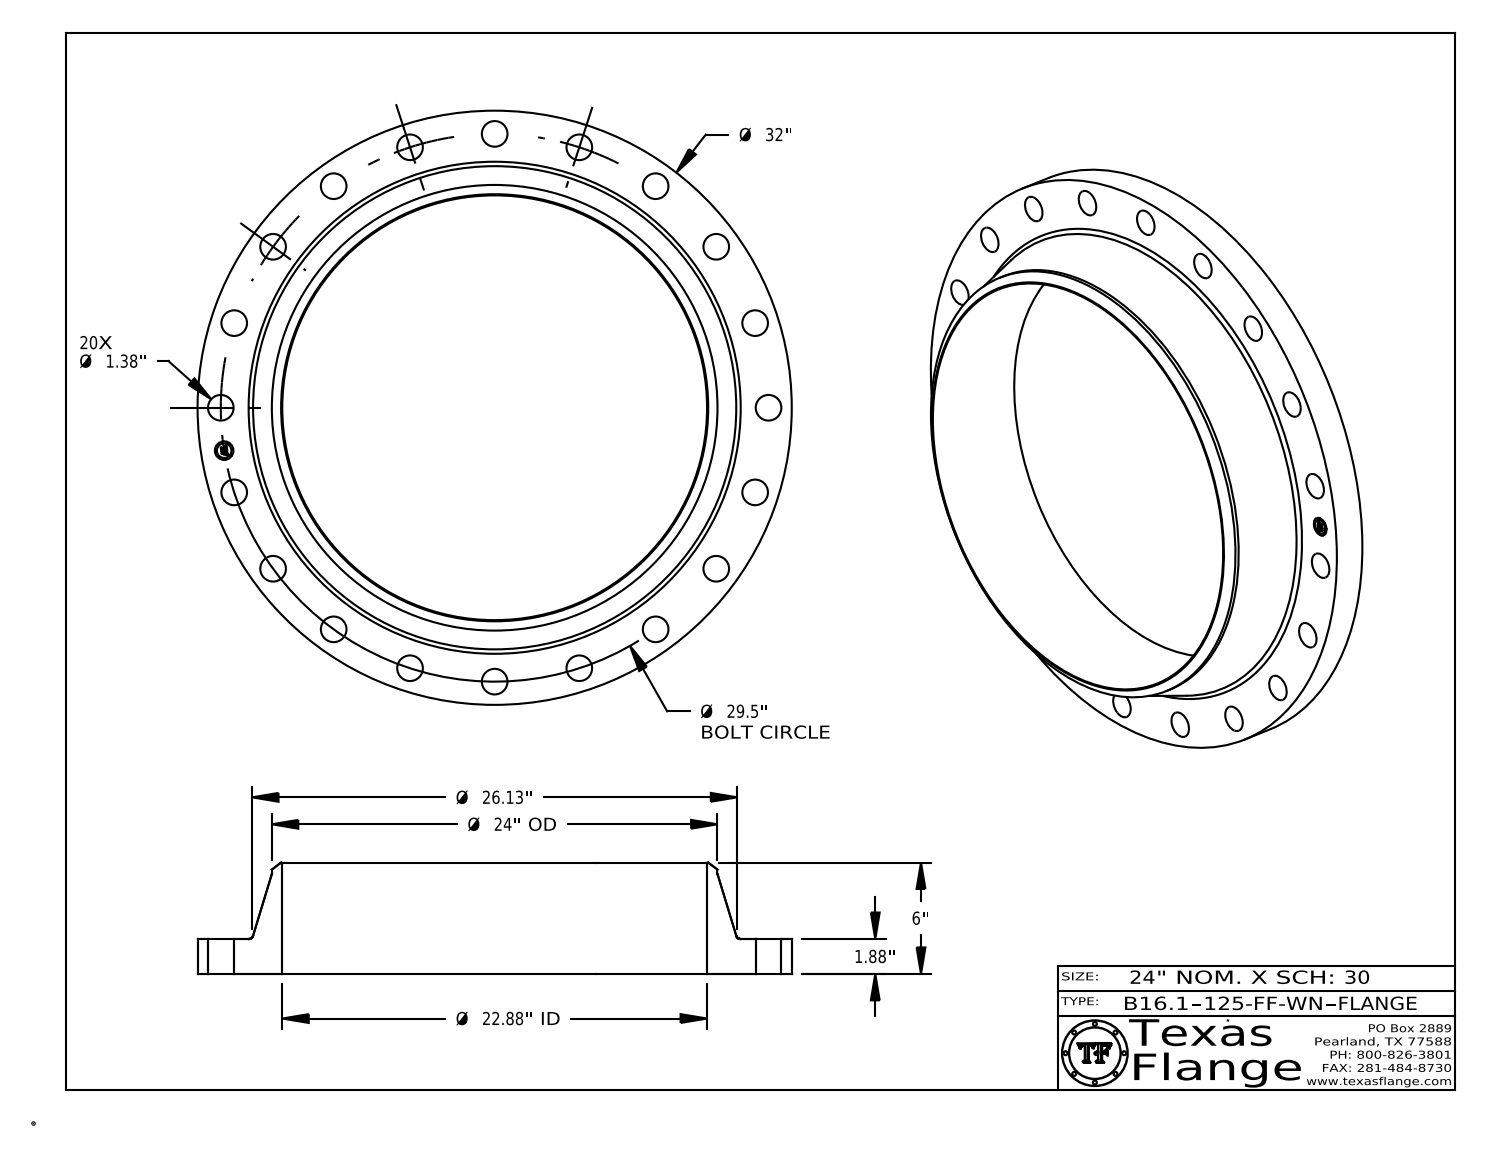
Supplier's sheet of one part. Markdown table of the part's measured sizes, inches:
| quantity | value |
| --- | --- |
| part name | B16.1, Class 125-FF-WN |
| STEP written by | CATIA V5 STEP AP214 (AUTOMOTIVE_DESIGN) |
| units | inches |
| bodies | 1 solid, 440 faces (368 planar, 66 cylindrical, 6 other) |
| overall size | 32 × 32 × 6 |
| volume | 991.7 in³ |
| surface area | 1 738 in² |
| round holes (diameter × count) | 1.38 × 20, 1 × 1, 22.876 × 1 |
| round bosses / shafts (diameter × count) | 0.061 × 8, 32 × 1, 24 × 1, 0.788 × 1 |
| main face-to-face distances | 1.88, 6, 4.12, 1.865, 0.015, 4.135, 0.298, 0.293, 0.054, 0.193 |
| hole center spacings | 14.75, 29.137, 4.615, 17.34, 20.859, 23.866, 26.285, 9.116 |
